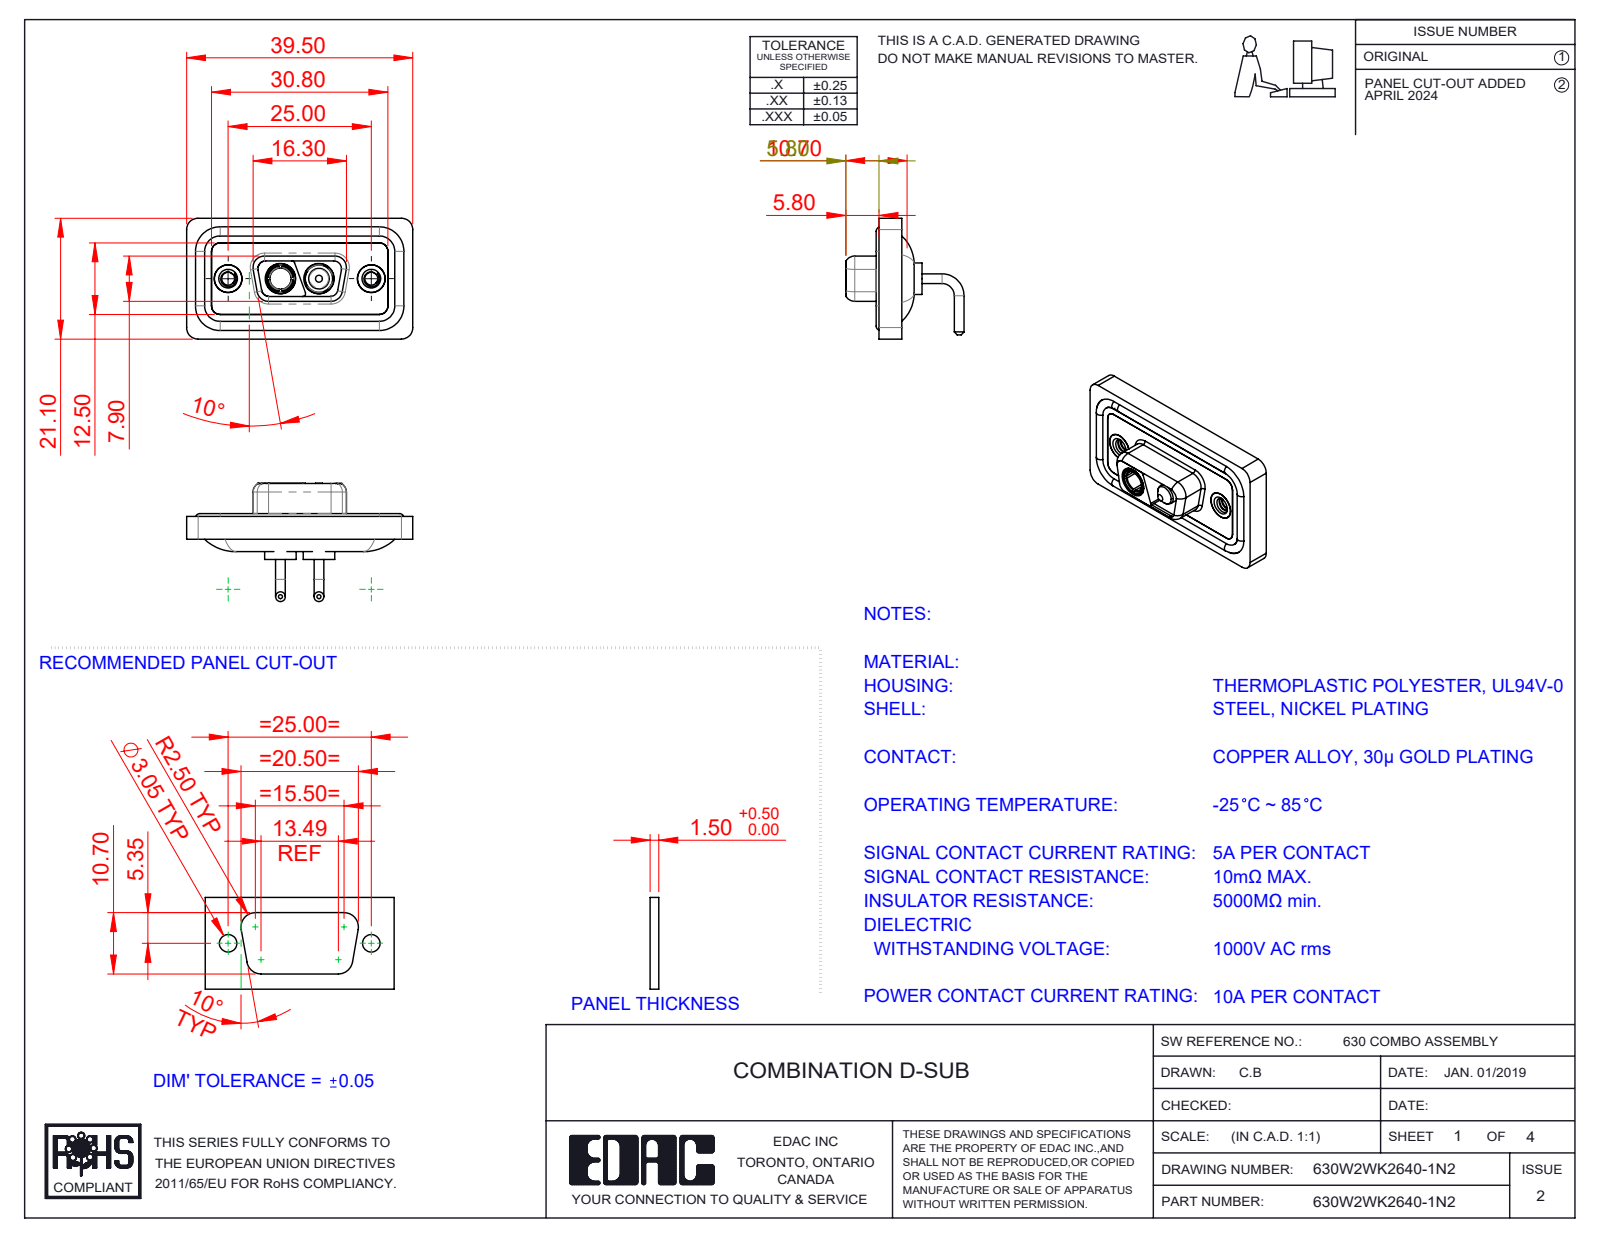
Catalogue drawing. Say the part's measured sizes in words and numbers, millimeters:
The part is named "630Combo Housing_2WK2; 630Combo Threaded Rivet_2; 630W2WK2640-1N2; 630Combo Shell Rear_09 Contacts (+4 more)". Its 3-D file was written by "SolidWorks 2023 (CONFIG_CONTROL_DESIGN)". It is 11 solids with 508 faces: 144 planar, 235 cylindrical and 129 other. Overall it measures 39.5 by 21.1 by 20.65 millimeters. Its volume is 4 591 cubic millimeters and its surface area 7 392 square millimeters. Round holes: 4 of diameter 4.85, 2 of diameter 2.26, 2 of diameter 4, 2 of diameter 4.05, 2 of diameter 5, 2 of diameter 5.3, 1 of diameter 3.7. Round bosses or shafts: 4 of diameter 1.7, 4 of diameter 1.6, 2 of diameter 5.5, 2 of diameter 5.2, 2 of diameter 4.95, 2 of diameter 4.8, 2 of diameter 4.75, 2 of diameter 3.75. Partial cylindrical surfaces (rounded edges, fillets, slot ends): 18 of radius 1.5, 18 of radius 2, 8 of radius 1.35, 8 of radius 1.6, 6 of radius 0.5, 4 of radius 0.25, 4 of radius 0.6, 4 of radius 0.65. The main face-to-face distances are 0.4, 1.1, 2.9, 1.8, 2.5, 1.6, 3.1, 1.5, 2.1, 3.7. The hole center spacings are 9.14, 15.86, 6.72, 25.
